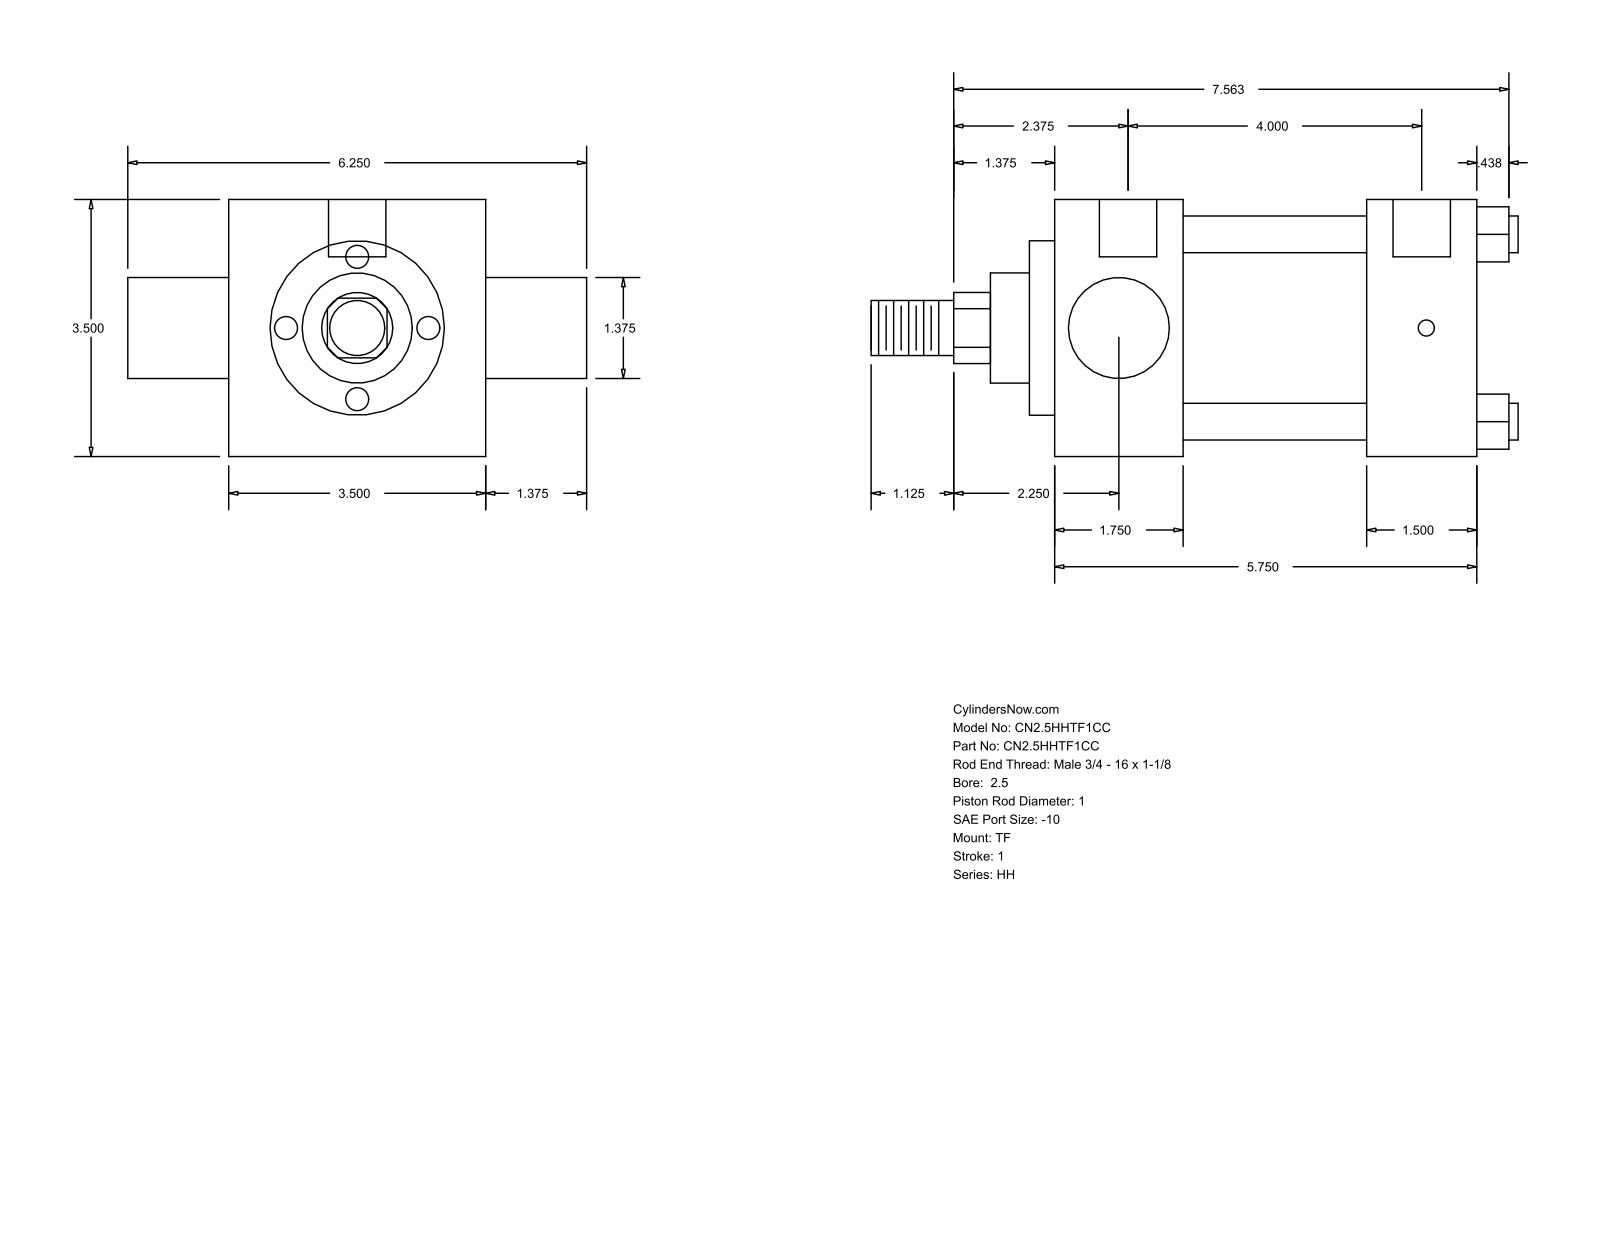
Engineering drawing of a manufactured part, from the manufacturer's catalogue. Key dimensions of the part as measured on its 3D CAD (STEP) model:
Part name (STEP PRODUCT): HH_TF__0250_1
STEP written by: GSSL Pune (CONFIG_CONTROL_DESIGN)
Units: millimetres
Bodies: 0 solids, 86 faces (61 planar, 25 cylindrical, 0 other)
Overall size (bounding box): 223.84 × 158.75 × 88.9
Round holes (diameter × count): ⌀5.56 ×3, ⌀19.84 ×2
Round bosses / shafts (diameter × count): ⌀12.7 ×4, ⌀73.03 ×1, ⌀60.33 ×1, ⌀38.1 ×1, ⌀34.92 ×1, ⌀25.4 ×1, ⌀19.05 ×1
Partial cylindrical surfaces — rounded edges, fillets, slot ends (radius × count): R12.29 ×1
Main face-to-face distances: 88.9, 146.05, 44.46, 101.59, 107.96, 63.5, 38.09, 34.93, 123.83, 8.73
Hole centre spacings: 1.58, 1.59, 101.6, 103.18, 103.19, 104.77
